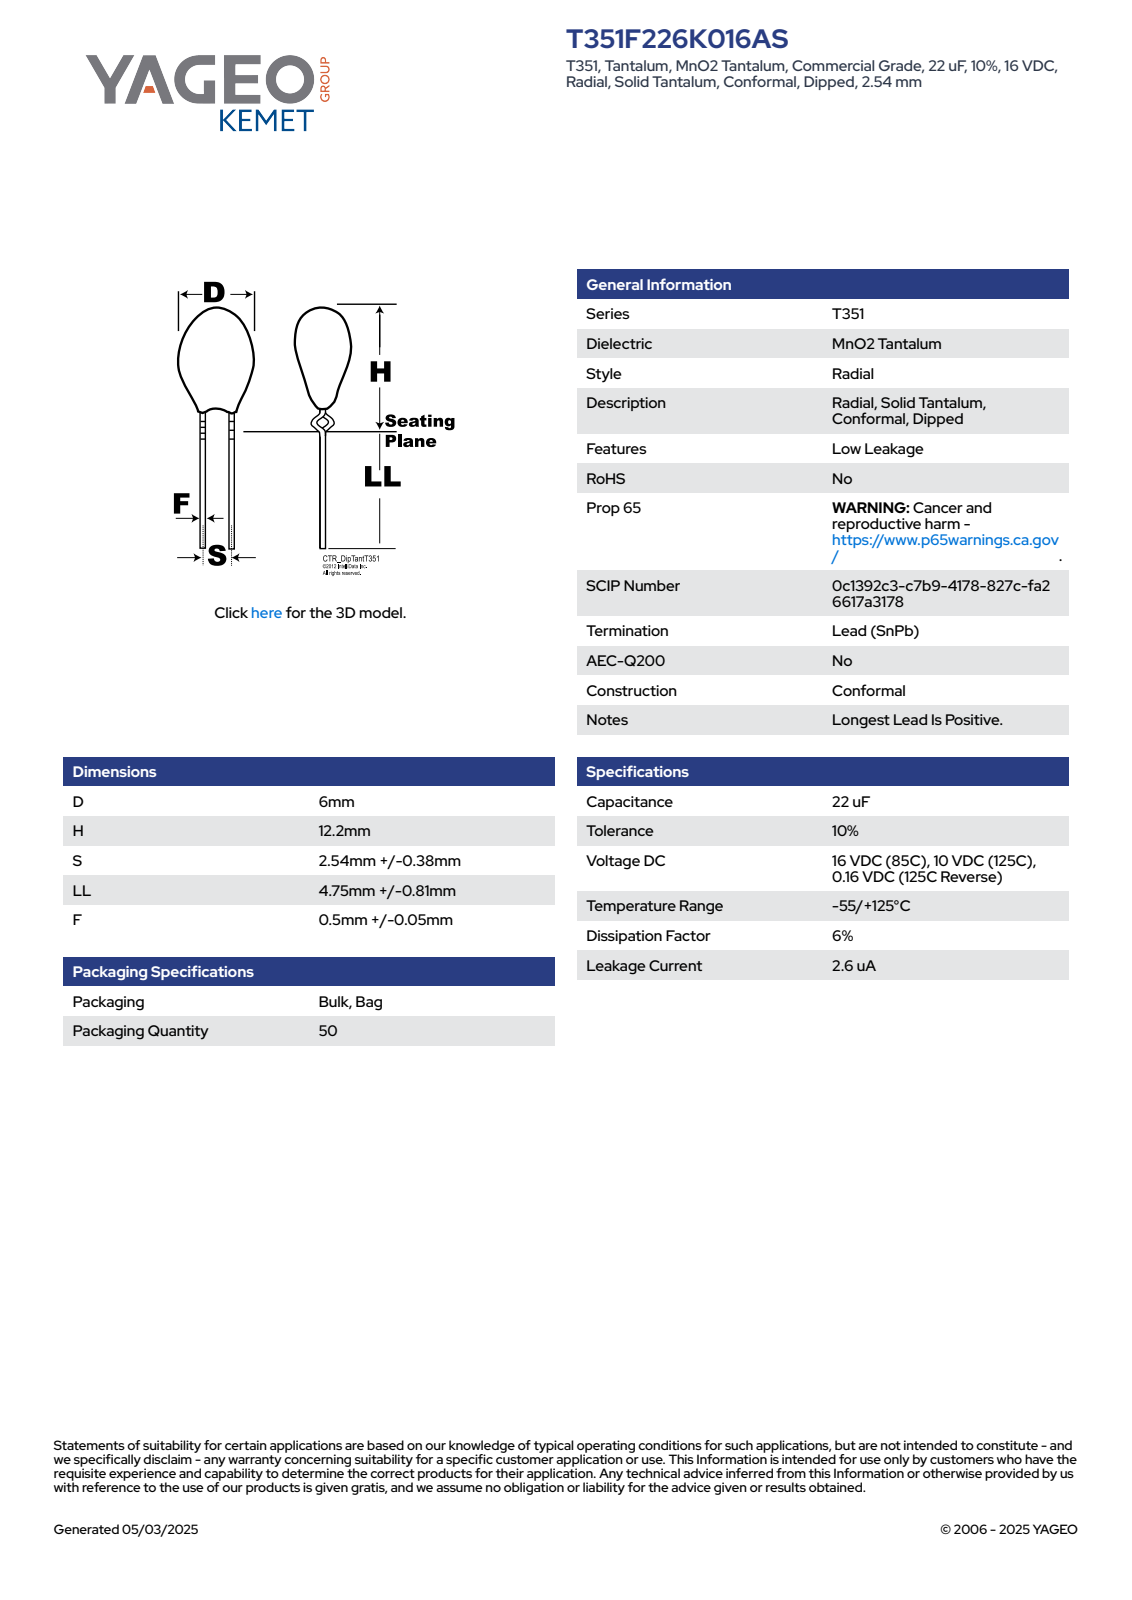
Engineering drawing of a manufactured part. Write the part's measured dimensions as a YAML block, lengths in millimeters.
part_name: "CTR_T351_D6H12.2S2.54LL5.56F0.55"
step_written_by: "SolidWorks 2014 (AUTOMOTIVE_DESIGN)"
units: millimeters
bodies: {solids: 1, faces: 88, planar: 27, cylindrical: 10, other: 51}
overall_size: [17.76, 6, 6]
volume: 199
surface_area: 204
round_bosses_or_shafts:
  - {diameter: 0.55, count: 2}
  - {diameter: 6, count: 1}
partial_cylinders:
  - {radius: 2.99, count: 1}
face_to_face_distances: [8.86, 13.58, 4.72, 12.78, 3.92, 0.8, 0.35, 0.65, 0.5, 12.93]
